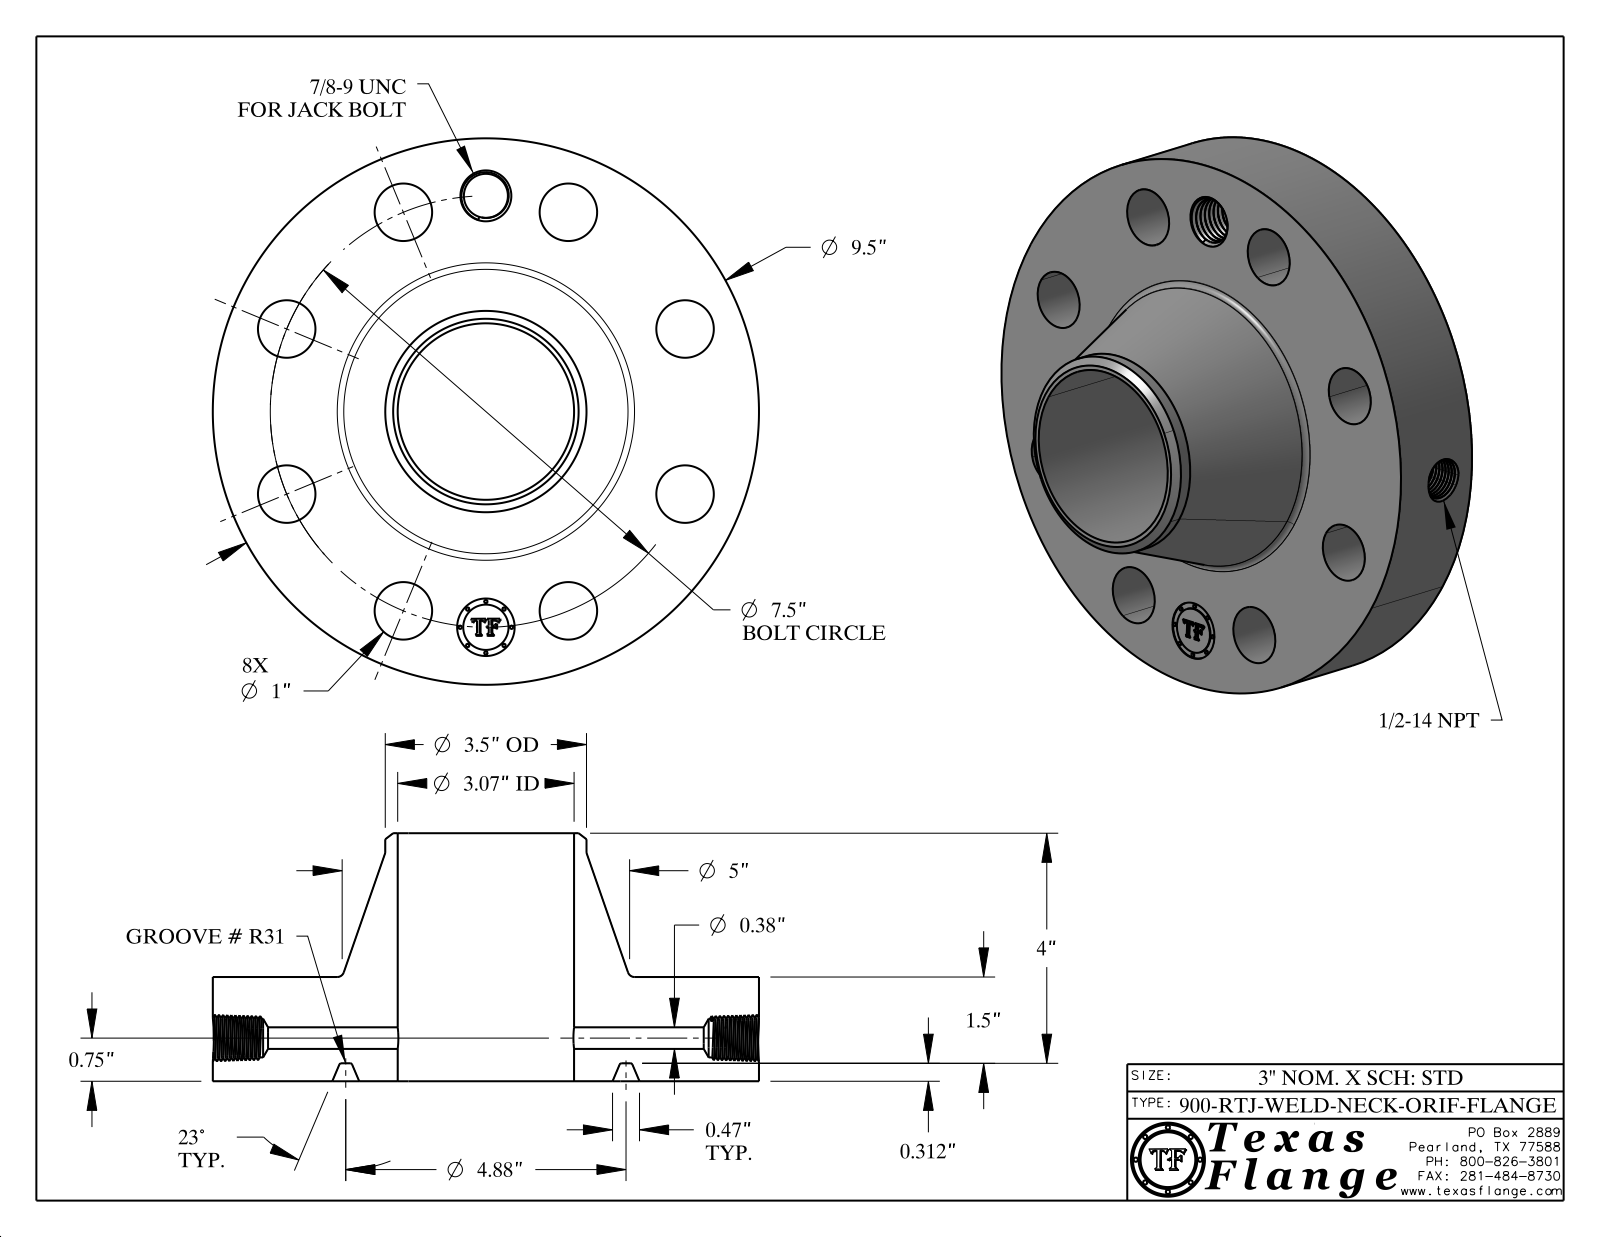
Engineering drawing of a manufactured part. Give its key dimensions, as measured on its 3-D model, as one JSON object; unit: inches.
{"part_name": "900-RTJ-WELD-NECK", "step_written_by": "CATIA V5 STEP AP214 (AUTOMOTIVE_DESIGN)", "units": "inches", "bodies": {"solids": 1, "faces": 784, "planar": 370, "cylindrical": 94, "other": 320}, "overall_size": [9.5, 9.5, 4.312], "volume_in3": 115.5, "surface_area_in2": 302.4, "round_holes": [[1, 9], [0.375, 1], [0.672, 1], [0.766, 1], [3.068, 1]], "round_bosses_or_shafts": [[0.061, 8], [9.5, 1], [3.5, 1], [0.788, 1]], "face_to_face_distances": [1.812, 0.312, 1.5, 4.312, 4, 2.5, 1.797, 1.485, 0.015, 2.515], "hole_center_spacings": [3.75, 2.87, 5.303, 6.929, 7.5, 1.463, 4.167, 6.236]}
